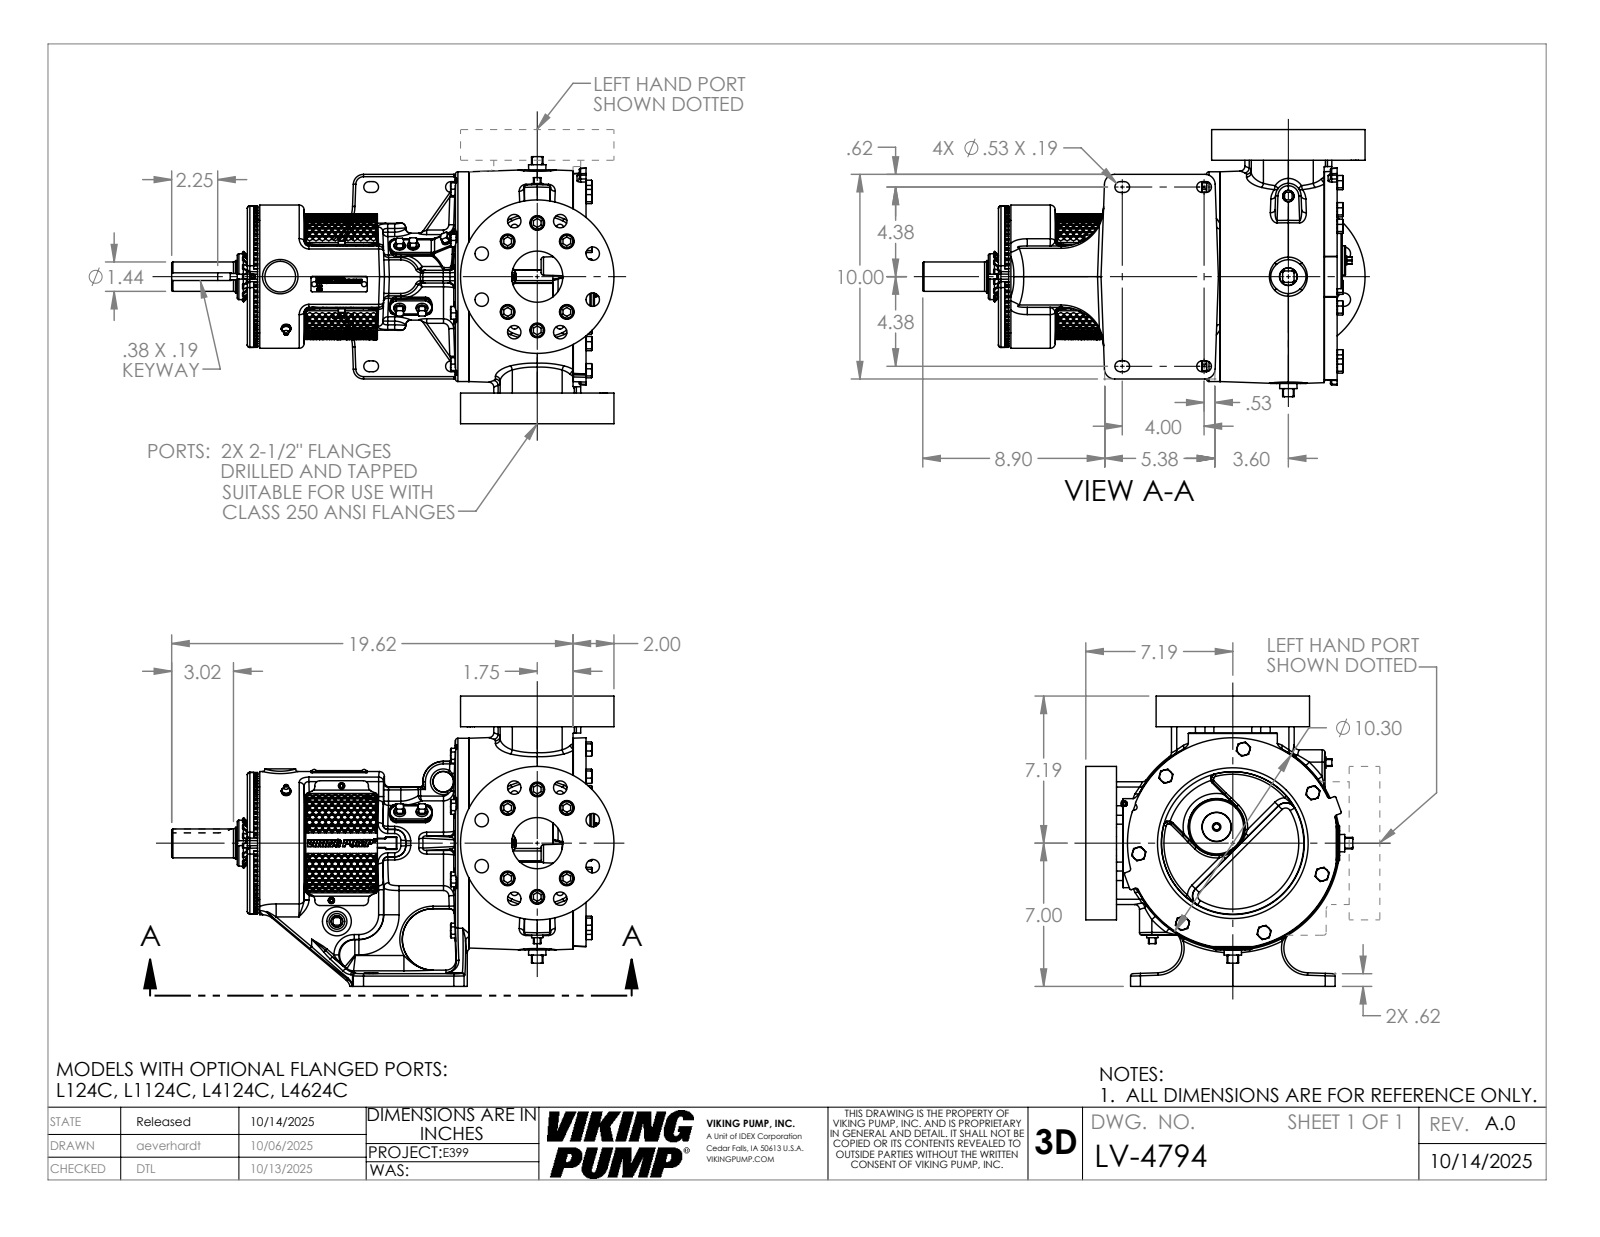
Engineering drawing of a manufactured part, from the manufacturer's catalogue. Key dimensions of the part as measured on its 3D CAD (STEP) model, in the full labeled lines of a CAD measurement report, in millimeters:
Part name (STEP PRODUCT): LV-4794
STEP written by: SolidWorks 2024 (AUTOMOTIVE_DESIGN)
Units: millimetres
Bodies: 1 solid, 4561 faces (1523 planar, 943 cylindrical, 2095 other)
Overall size (bounding box): 549.2 × 360.4 × 331.5
Volume: 15 140 000 mm³ · Surface area: 900 000 mm²
Round holes (diameter × count): ⌀16.7 ×16, ⌀18.3 ×12, ⌀6.4 ×9, ⌀27.8 ×8, ⌀5.1 ×6, ⌀4 ×3, ⌀6.8 ×2, ⌀8 ×2, ⌀63.5 ×2, ⌀11.5 ×1, ⌀40.1 ×1, ⌀40.5 ×1
Round bosses / shafts (diameter × count): ⌀16.8 ×12, ⌀15.9 ×10, ⌀15.9 ×5, ⌀7.9 ×3, ⌀4.8 ×3, ⌀190.5 ×2, ⌀260.4 ×1, ⌀177.8 ×1
Partial cylindrical surfaces — rounded edges, fillets, slot ends (radius × count): R1.6 ×109, R3 ×78, R1.8 ×74, R6.1 ×48, R0.8 ×18, R25.4 ×16, R1.5 ×14, R6.4 ×14
Main face-to-face distances: 38.1, 360.3, 322.2, 350.7, 89.8, 260.9, 12.7, 57.2, 54.4, 144.3
Hole centre spacings: 57.1, 76.2, 74.6, 137.9, 34.9, 26.4, 35.6, 55.4
